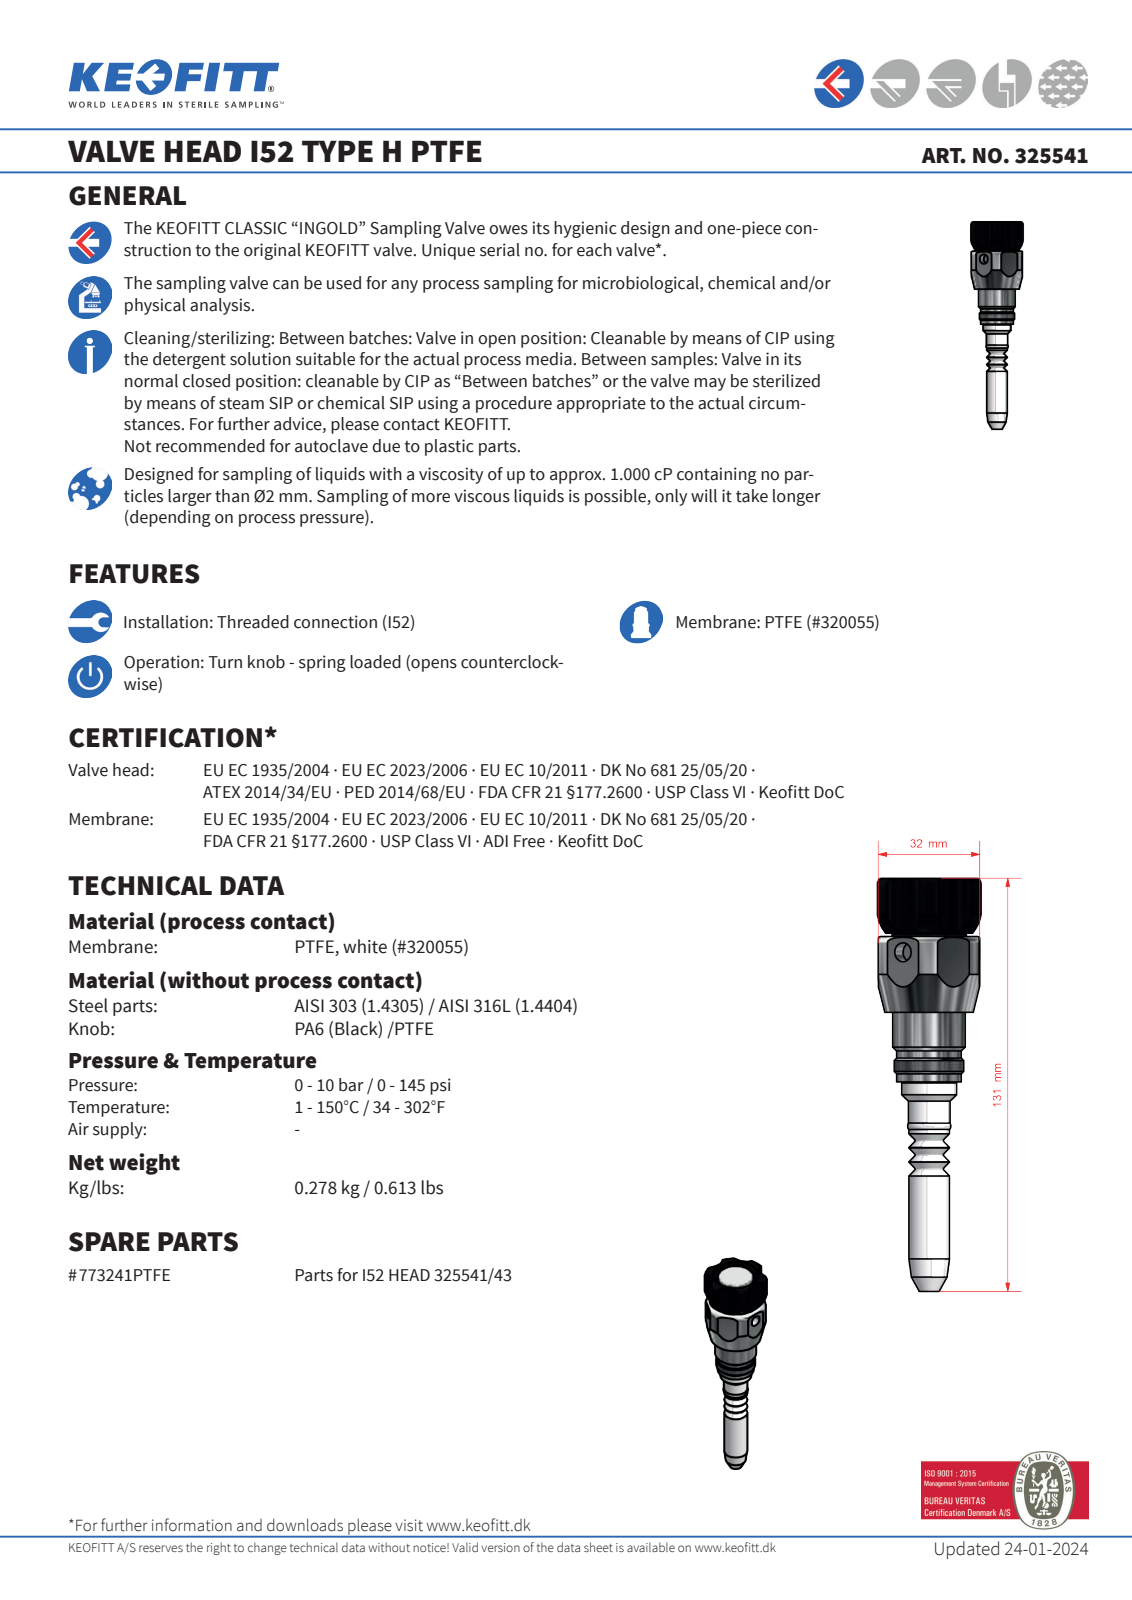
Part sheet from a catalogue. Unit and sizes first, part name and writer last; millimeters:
Units: millimetres
Overall size (bounding box): 130.5 × 35 × 33.66
Round bosses / shafts (diameter × count): ⌀24 ×1, ⌀23 ×1, ⌀22 ×1, ⌀20.5 ×1, ⌀17.5 ×1, ⌀13.2 ×1, ⌀12.9 ×1
Partial cylindrical surfaces — rounded edges, fillets, slot ends (radius × count): R8 ×6, R17 ×1, R17.5 ×1
Main face-to-face distances: 32.02, 18.5, 24, 42.5, 32, 25, 1, 17.5, 22, 46
Volume: 49 745 mm³ · Surface area: 10 603 mm²
Bodies: 1 solid, 72 faces (12 planar, 29 cylindrical, 31 other)
Part name (STEP PRODUCT): 325541
STEP written by: Autodesk Inventor 2022 (AUTOMOTIVE_DESIGN)
